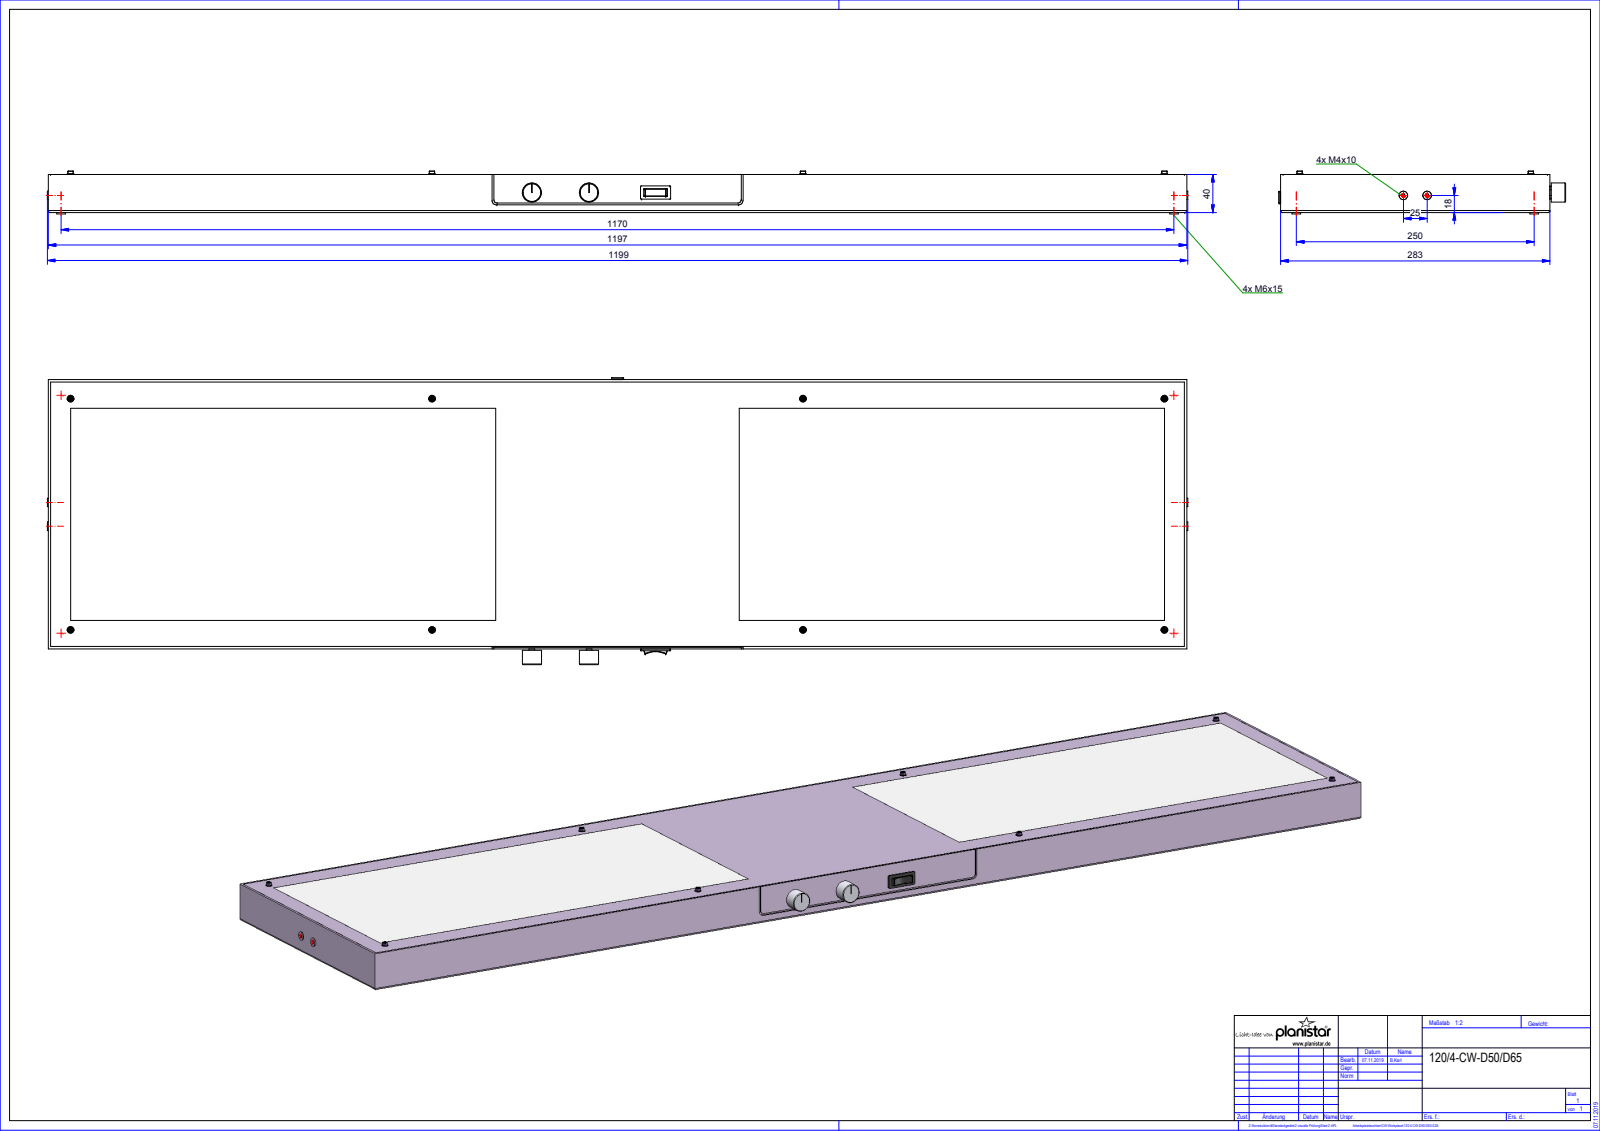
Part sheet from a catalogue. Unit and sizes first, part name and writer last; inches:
Units: inches
Overall size (bounding box): 47.205 × 11.87 × 1.776
Round holes (diameter × count): ⌀0.126 ×8, ⌀0.197 ×4, ⌀0.236 ×4, ⌀0.13 ×2, ⌀0.157 ×2, ⌀0.22 ×1, ⌀0.394 ×1
Round bosses / shafts (diameter × count): ⌀0.276 ×8, ⌀0.217 ×8, ⌀0.118 ×8, ⌀0.097 ×8, ⌀0.354 ×6, ⌀0.787 ×2, ⌀0.236 ×2, ⌀0.496 ×1
Partial cylindrical surfaces — rounded edges, fillets, slot ends (radius × count): R0.009 ×48, R0.023 ×48, R0.02 ×6, R0.039 ×4, R0.079 ×4, R0.138 ×2, R0.197 ×2, R0.957 ×1
Main face-to-face distances: 1.577, 1.579, 11.142, 0.079, 11.063, 47.126, 1.575, 0.138, 0.591, 0.02
Hole centre spacings: 0.417, 9.567, 9.713, 14.961, 15.355, 17.758, 18.164, 30.315
Volume: 828.7 in³ · Surface area: 1 273 in²
Bodies: 22 solids, 350 faces (127 planar, 188 cylindrical, 35 other)
Part name (STEP PRODUCT): Root; Baugruppe_Xled-2-VD; QUADER_0; ISO 14579-M3x10-10.9_Zylinderkopfschrauben (+4 more)
STEP written by: HiCAD 2015 2002.1 Build 408 (AUTOMOTIVE_DESIGN)
